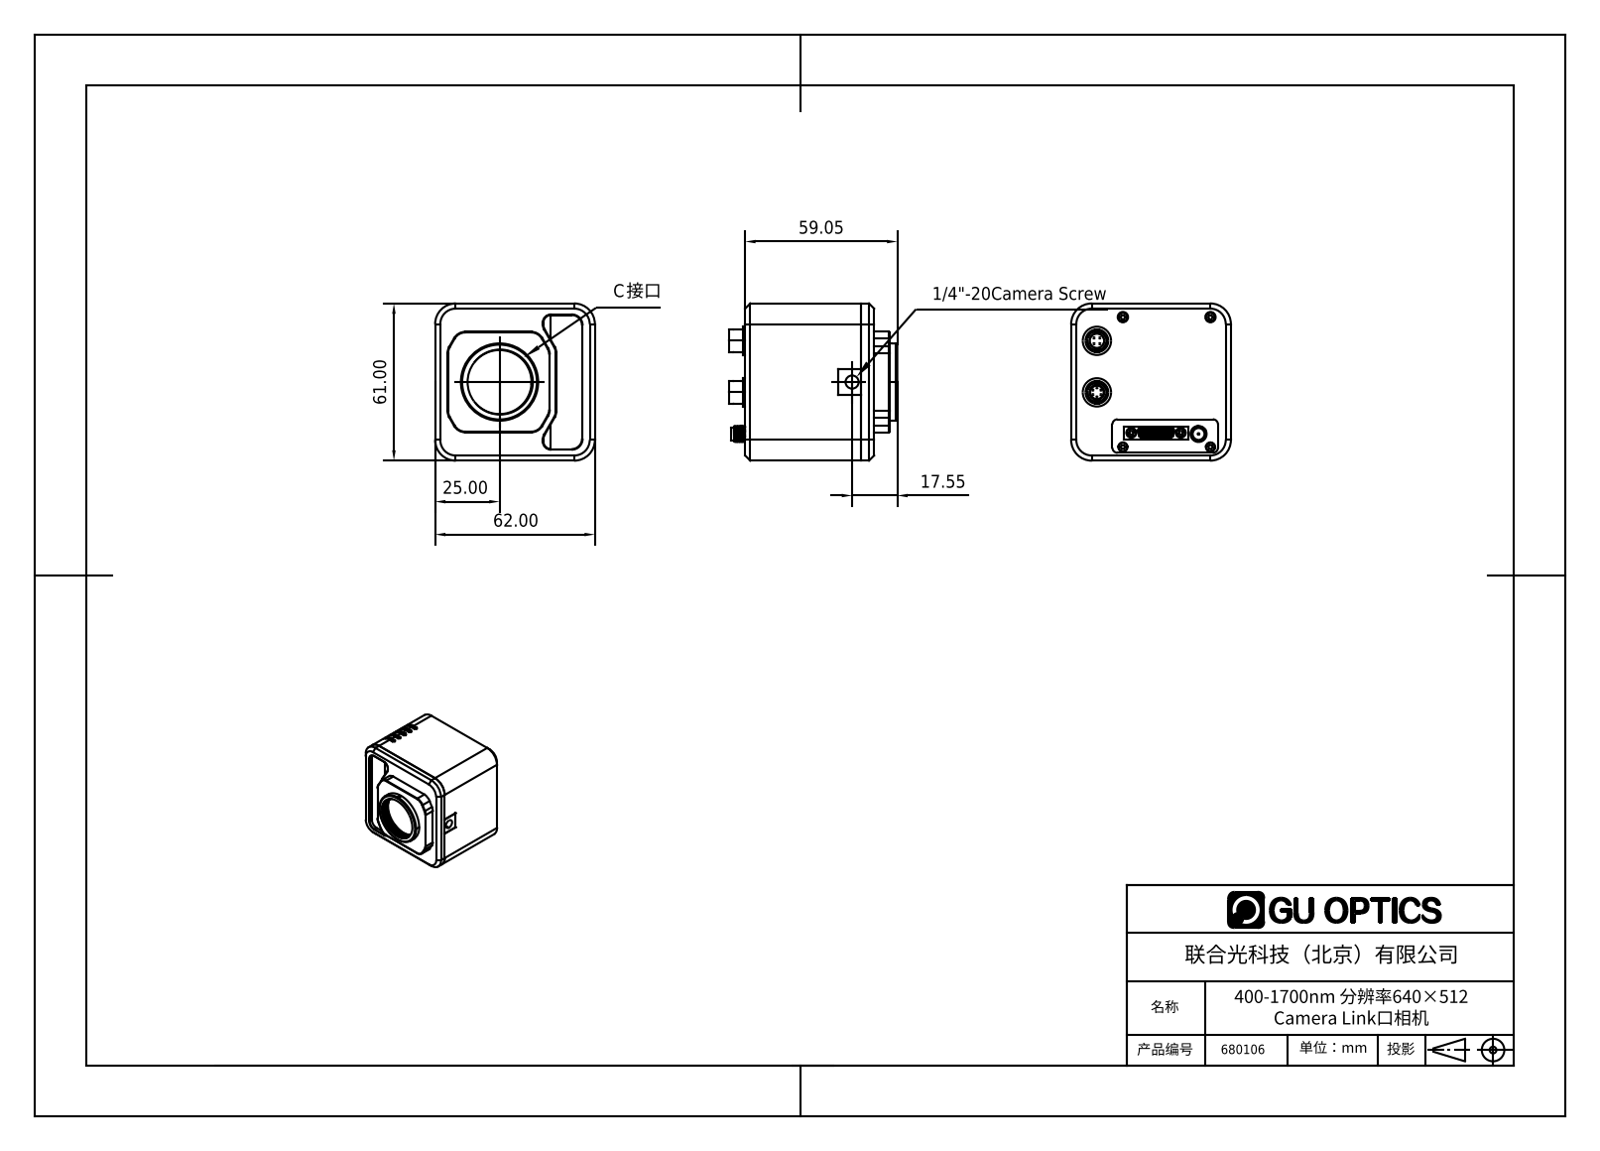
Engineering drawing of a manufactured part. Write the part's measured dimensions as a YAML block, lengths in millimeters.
part_name: "680106"
step_written_by: "SolidWorks 2020 (CONFIG_CONTROL_DESIGN)"
units: millimeters
bodies: {solids: 11, faces: 2047, planar: 1157, cylindrical: 714, other: 176}
overall_size: [65.35, 62, 61]
volume: 209156
surface_area: 42726
round_holes:
  - {diameter: 2, count: 27}
  - {diameter: 0.8, count: 14}
  - {diameter: 1.5, count: 11}
  - {diameter: 1.6, count: 9}
  - {diameter: 4, count: 6}
  - {diameter: 2.2, count: 4}
  - {diameter: 5.7, count: 2}
  - {diameter: 6.6, count: 2}
  - {diameter: 7.4, count: 2}
  - {diameter: 7.8, count: 2}
  - {diameter: 8, count: 2}
  - {diameter: 8.1, count: 2}
round_bosses_or_shafts:
  - {diameter: 0.46, count: 10}
  - {diameter: 1.2, count: 9}
  - {diameter: 1.1, count: 6}
  - {diameter: 3.6, count: 4}
  - {diameter: 2, count: 4}
  - {diameter: 11, count: 2}
  - {diameter: 9.4, count: 2}
  - {diameter: 8.85, count: 2}
partial_cylinders:
  - {radius: 4.1, count: 24}
  - {radius: 1, count: 17}
  - {radius: 2, count: 16}
  - {radius: 0.25, count: 15}
  - {radius: 5, count: 9}
  - {radius: 0.2, count: 8}
  - {radius: 0.3, count: 8}
  - {radius: 0.6, count: 8}
face_to_face_distances: [45, 45.05, 2, 61, 5, 9, 62, 9.05, 36, 6]
hole_center_spacings: [4.74, 3, 10.55, 12.38, 15.21, 6.02, 6.36, 8.32]
